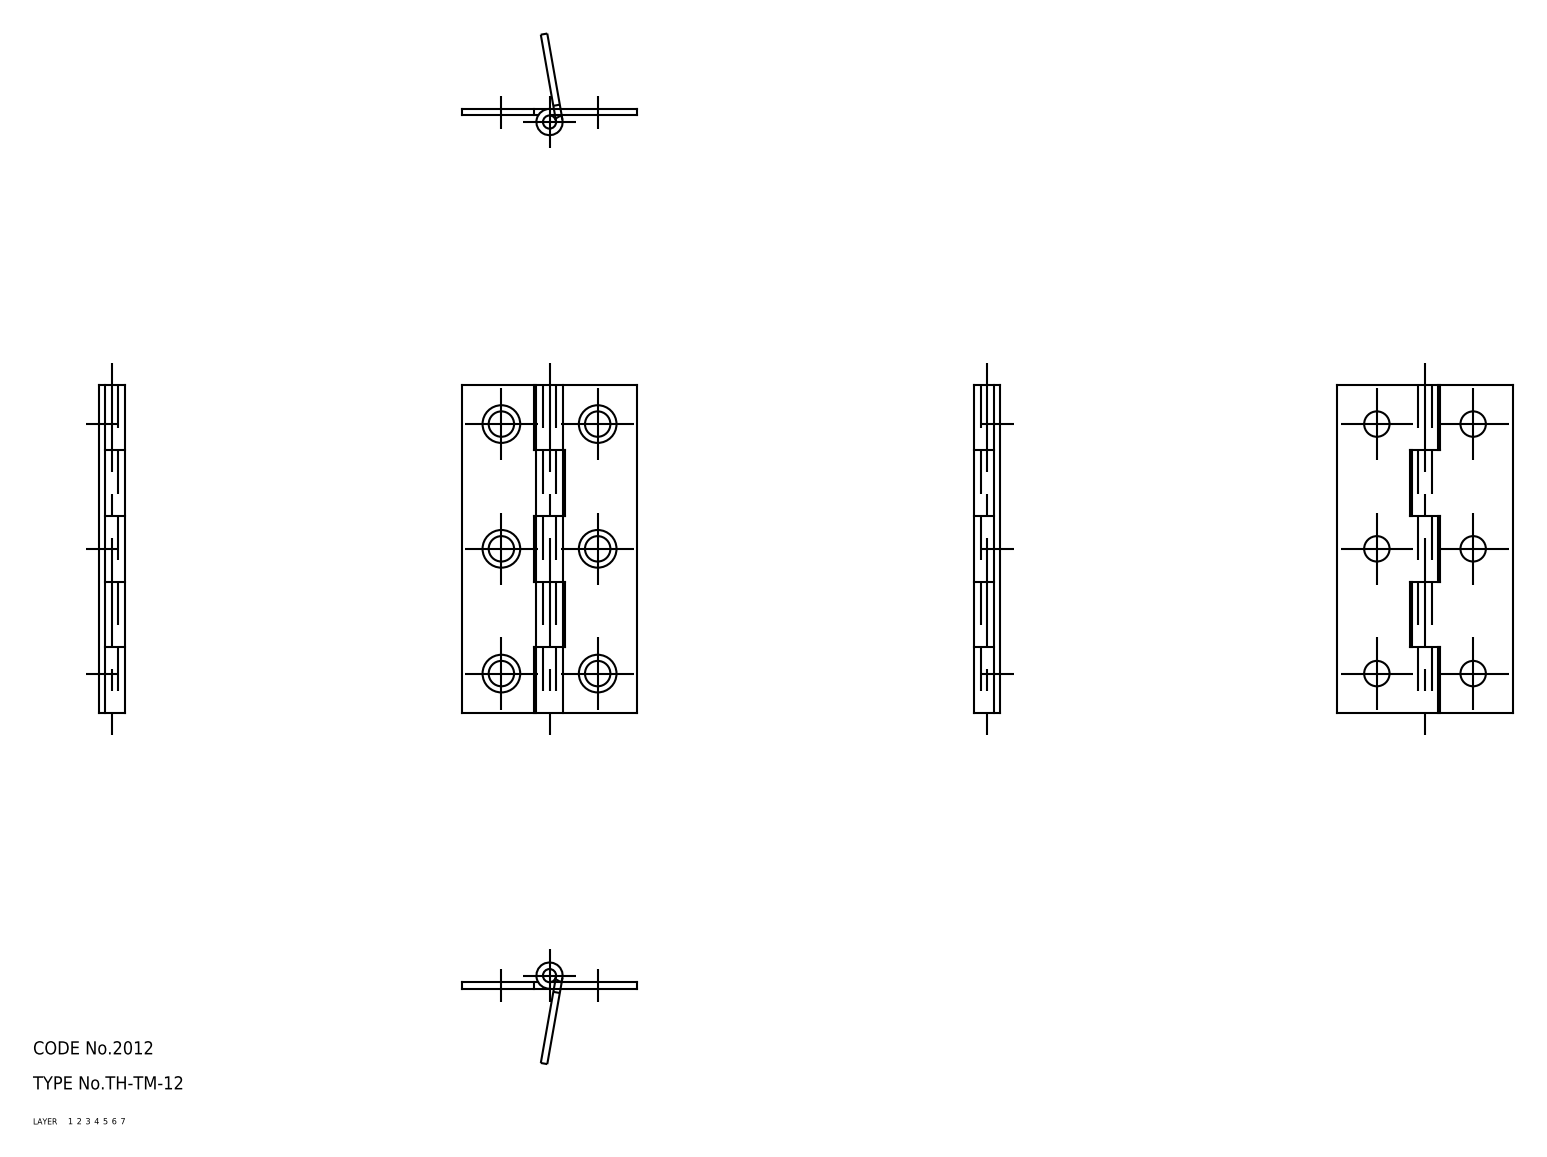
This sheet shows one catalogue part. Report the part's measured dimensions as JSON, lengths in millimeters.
{"part_name": "shaft; hinge piece_B; hinge piece_A; TH_TM_12_21278_36", "step_written_by": "CADfix (AUTOMOTIVE_DESIGN)", "units": "millimeters", "bodies": {"solids": 3, "faces": 66, "planar": 0, "cylindrical": 0, "other": 66}, "overall_size": [75, 40, 6], "volume_mm3": 5595, "surface_area_mm2": 8508}
